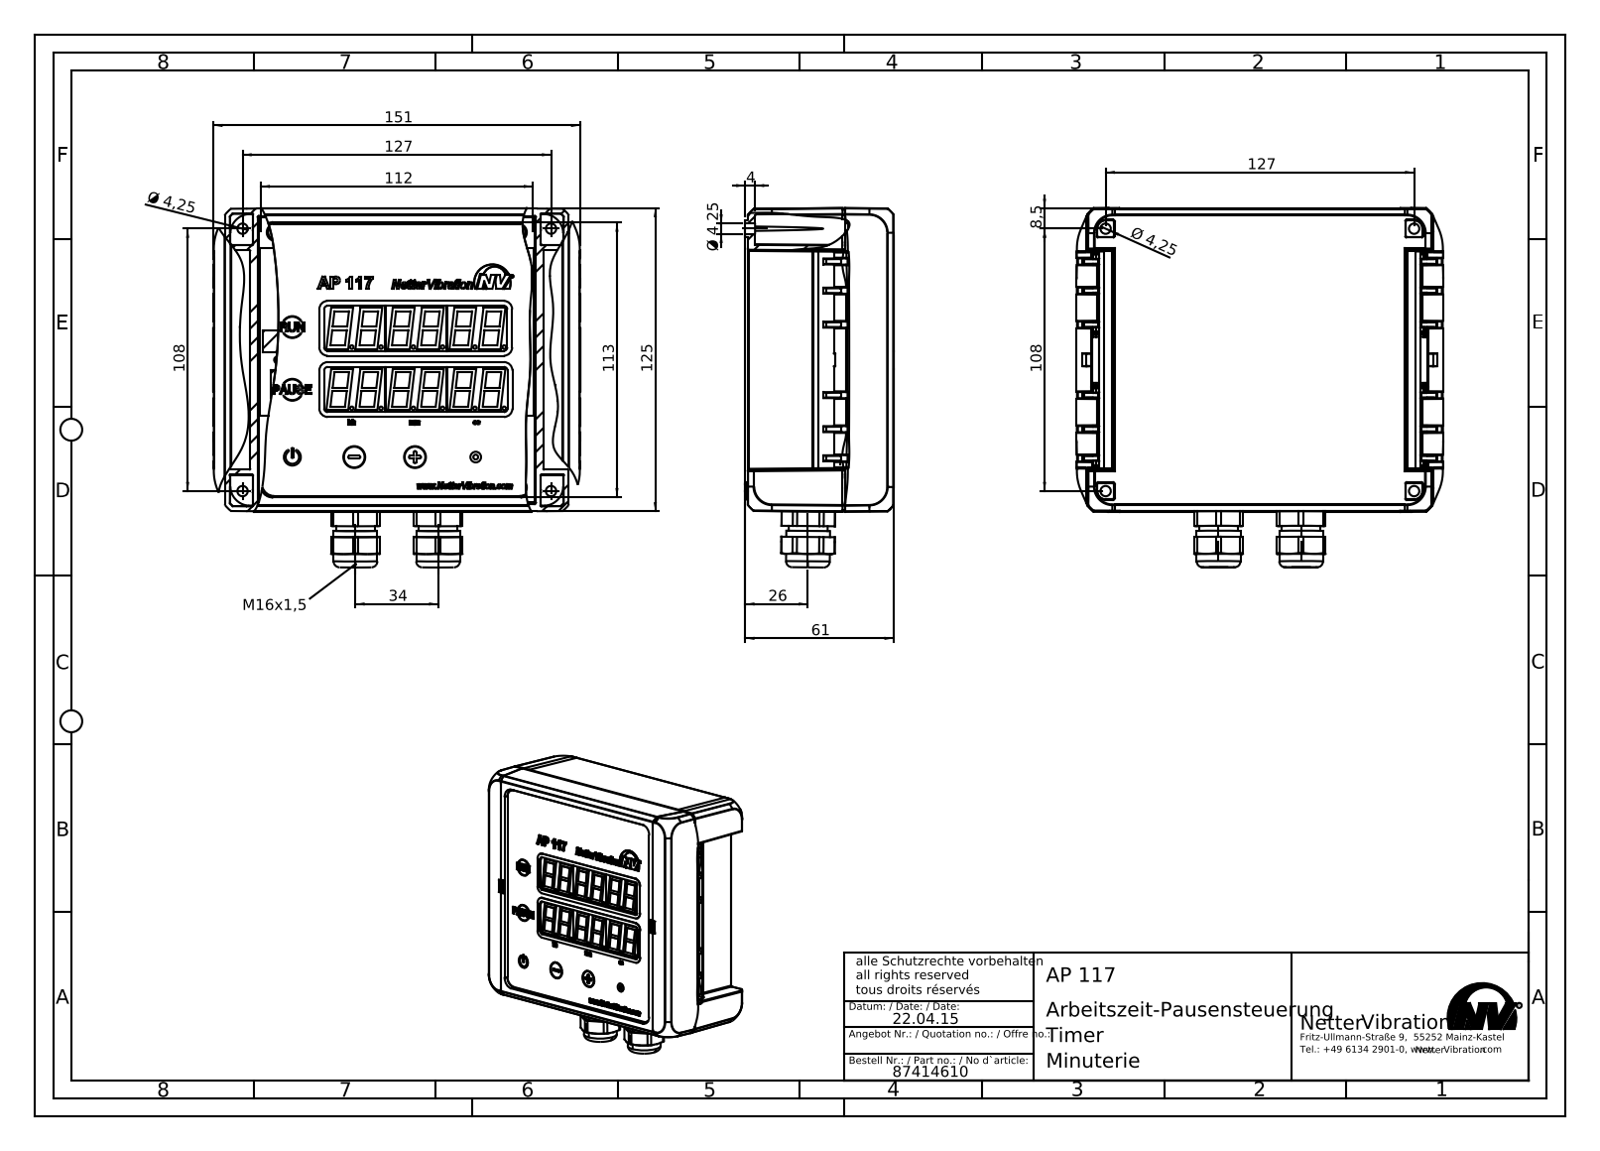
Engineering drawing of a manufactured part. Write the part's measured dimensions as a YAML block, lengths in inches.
part_name: "AP117 #87414610"
step_written_by: "SolidWorks 2015 (AUTOMOTIVE_DESIGN)"
units: inches
bodies: {solids: 10, faces: 4181, planar: 1663, cylindrical: 1073, other: 1445}
overall_size: [5.945, 5.824, 2.402]
volume: 17.36
surface_area: 339.1
round_holes:
  - {diameter: 0.059, count: 12}
  - {diameter: 0.079, count: 5}
  - {diameter: 0.167, count: 4}
  - {diameter: 0.236, count: 2}
  - {diameter: 0.315, count: 2}
  - {diameter: 0.335, count: 2}
  - {diameter: 0.545, count: 2}
  - {diameter: 0.65, count: 2}
  - {diameter: 0.035, count: 1}
  - {diameter: 0.217, count: 1}
round_bosses_or_shafts:
  - {diameter: 0.63, count: 4}
  - {diameter: 0.709, count: 2}
  - {diameter: 0.496, count: 2}
  - {diameter: 0.354, count: 2}
  - {diameter: 0.157, count: 2}
  - {diameter: 0.276, count: 1}
  - {diameter: 0.173, count: 1}
  - {diameter: 0.044, count: 1}
partial_cylinders:
  - {radius: 0.012, count: 220}
  - {radius: 0.02, count: 202}
  - {radius: 0.039, count: 30}
  - {radius: 0.079, count: 16}
  - {radius: 0.008, count: 12}
  - {radius: 0.591, count: 12}
  - {radius: 0.005, count: 8}
  - {radius: 0.059, count: 8}
face_to_face_distances: [0.118, 2.165, 2.283, 0.02, 0.354, 2.047, 1.744, 0.303, 1.862, 0.421]
hole_center_spacings: [0.998, 1.407, 0.472, 0.992, 1.099, 0.526, 0.839, 1.123]
